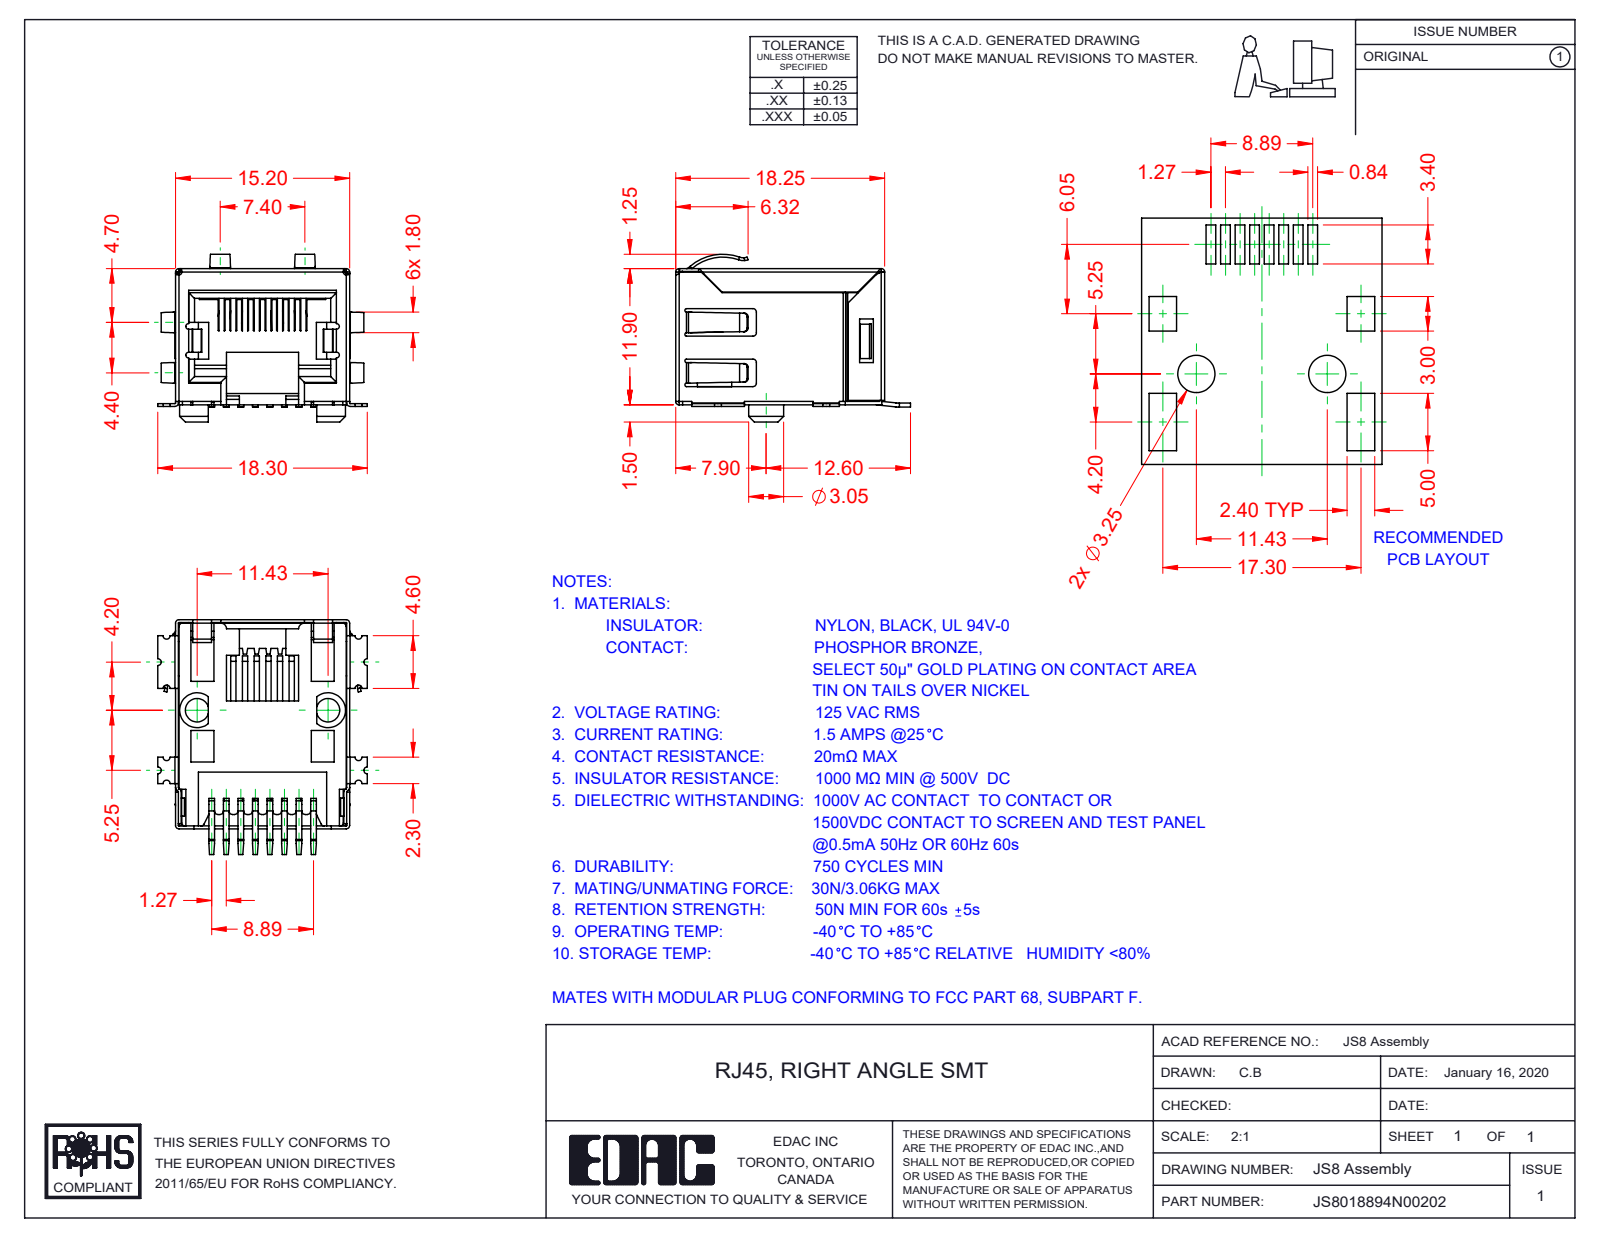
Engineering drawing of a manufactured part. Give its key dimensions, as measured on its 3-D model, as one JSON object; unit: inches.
{"part_name": "S8 Contacts; S8 Insulator; S8 Shield; RJS8018894N00202", "step_written_by": "SolidWorks 2016 (CONFIG_CONTROL_DESIGN)", "units": "inches", "bodies": {"solids": 10, "faces": 976, "planar": 602, "cylindrical": 314, "other": 60}, "overall_size": [0.807, 0.72, 0.577], "volume_in3": 0.08, "surface_area_in2": 7.183, "partial_cylinders_radius": [[0.012, 59], [0.01, 19], [0.02, 18], [0.008, 17], [0.006, 8], [0.03, 7], [0.039, 4], [0.049, 3]], "face_to_face_distances": [0.577, 0.589, 0.587, 0.039, 0.014, 0.579, 0.03, 0.429, 0.043, 0.598]}
